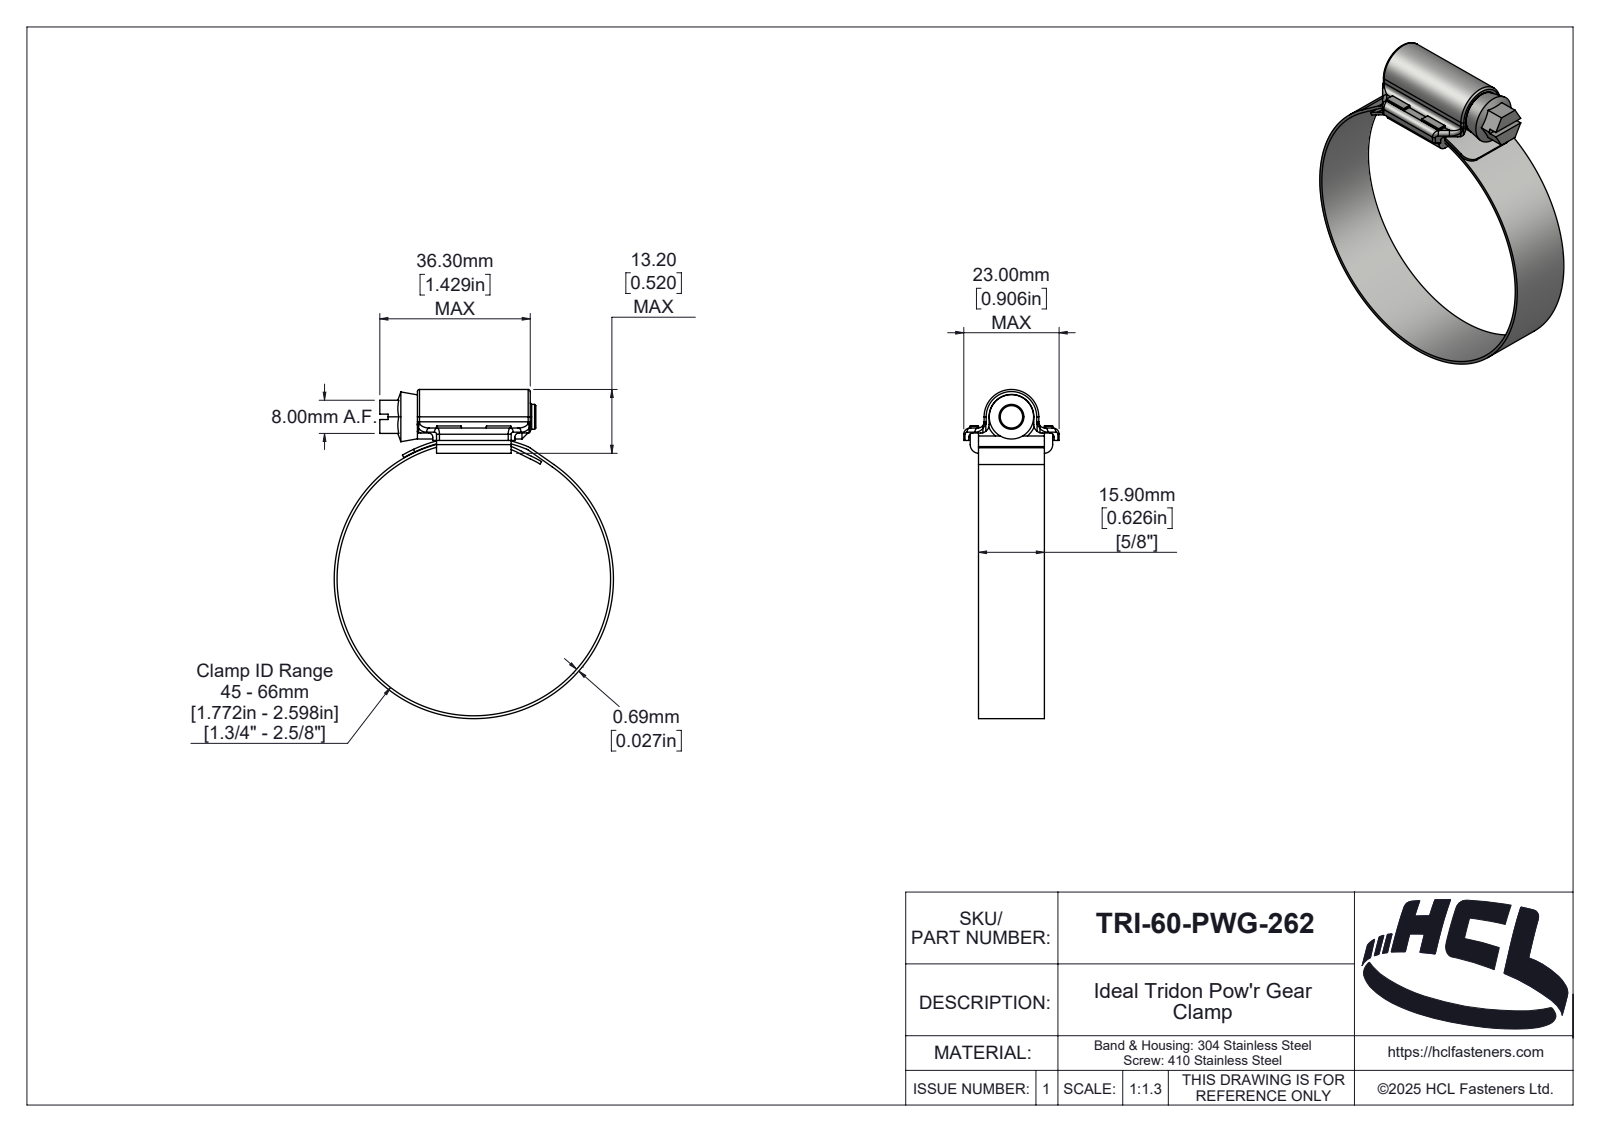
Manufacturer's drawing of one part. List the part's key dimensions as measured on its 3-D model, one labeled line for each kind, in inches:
Part name (STEP PRODUCT): TRI-60-PWG-262
STEP written by: SolidWorks 2025 (AUTOMOTIVE_DESIGN)
Units: inches
Bodies: 4 solids, 268 faces (87 planar, 102 cylindrical, 79 other)
Overall size (bounding box): 3.126 × 2.653 × 0.906
Volume: 0.481 in³ · Surface area: 19.73 in²
Round holes (diameter × count): ⌀2.598 ×1
Round bosses / shafts (diameter × count): ⌀2.653 ×1, ⌀0.421 ×1, ⌀0.236 ×1
Partial cylindrical surfaces — rounded edges, fillets, slot ends (radius × count): R0.039 ×14, R0.02 ×4, R0.059 ×4, R0.079 ×3, R0.004 ×2, R0.083 ×2, R0.118 ×2, R0.018 ×1
Main face-to-face distances: 0.079, 0.626, 0.705, 0.193, 0.047, 0.179, 0.132, 0.027, 0.604, 0.1
